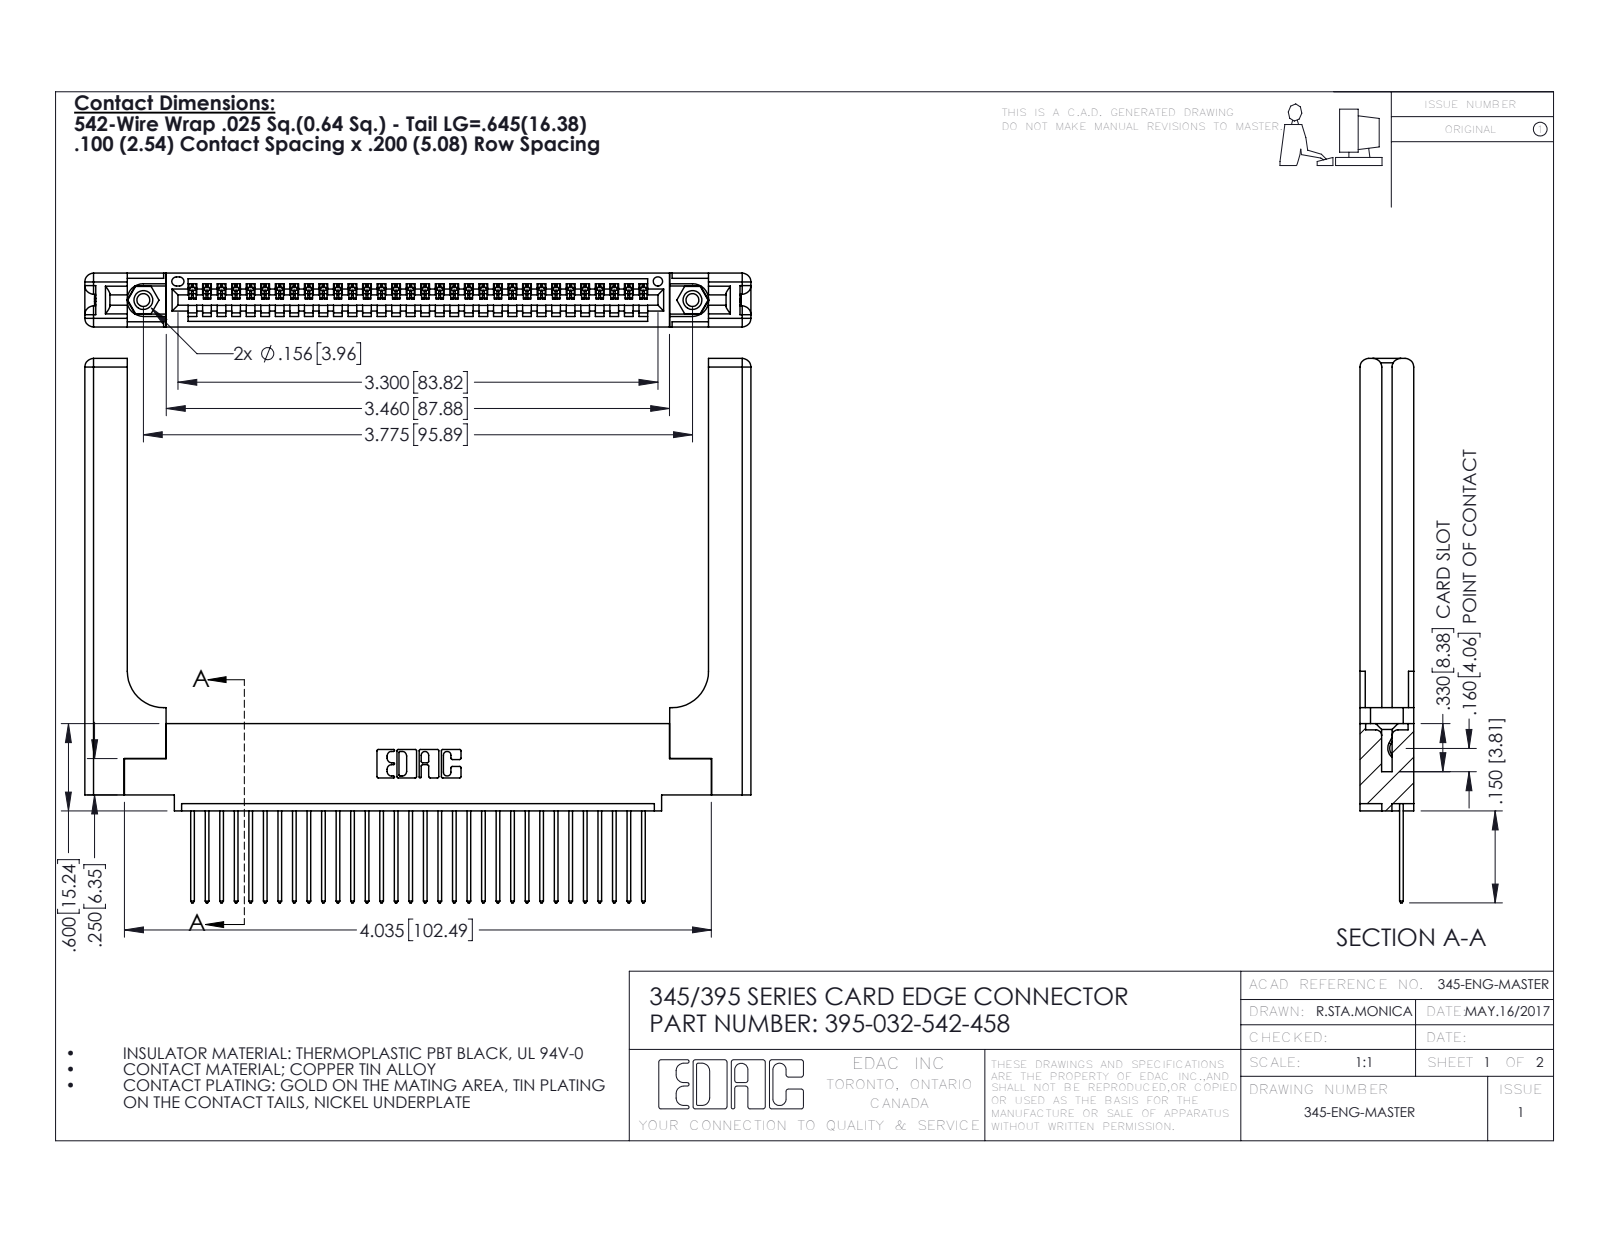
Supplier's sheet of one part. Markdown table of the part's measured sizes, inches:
| quantity | value |
| --- | --- |
| part name | 345-250-001_345-250-001-102; 395-032-542-458; 345-220-058_345-220-058; 345-292-001_345-293-142 (+1 more) |
| STEP written by | SolidWorks 2016 (CONFIG_CONTROL_DESIGN) |
| units | inches |
| bodies | 37 solids, 2242 faces (1512 planar, 670 cylindrical, 60 other) |
| overall size | 4.579 × 3.742 × 0.37 |
| volume | 1.188 in³ |
| surface area | 31.42 in² |
| round holes (diameter × count) | 0.089 × 2, 0.125 × 2, 0.156 × 2, 0.064 × 1 |
| round bosses / shafts (diameter × count) | 0.155 × 2 |
| partial cylindrical surfaces (radius × count) | 0.006 × 64, 0.01 × 64, 0.01 × 22, 0.06 × 16, 0.007 × 6, 0.031 × 6, 0.026 × 3, 0.03 × 2 |
| main face-to-face distances | 0.37, 0.072, 0.298, 0.098, 0.272, 0.025, 0.2, 0.148, 0.15, 0.077 |
| hole center spacings | 0.27, 3.54, 3.775 |
